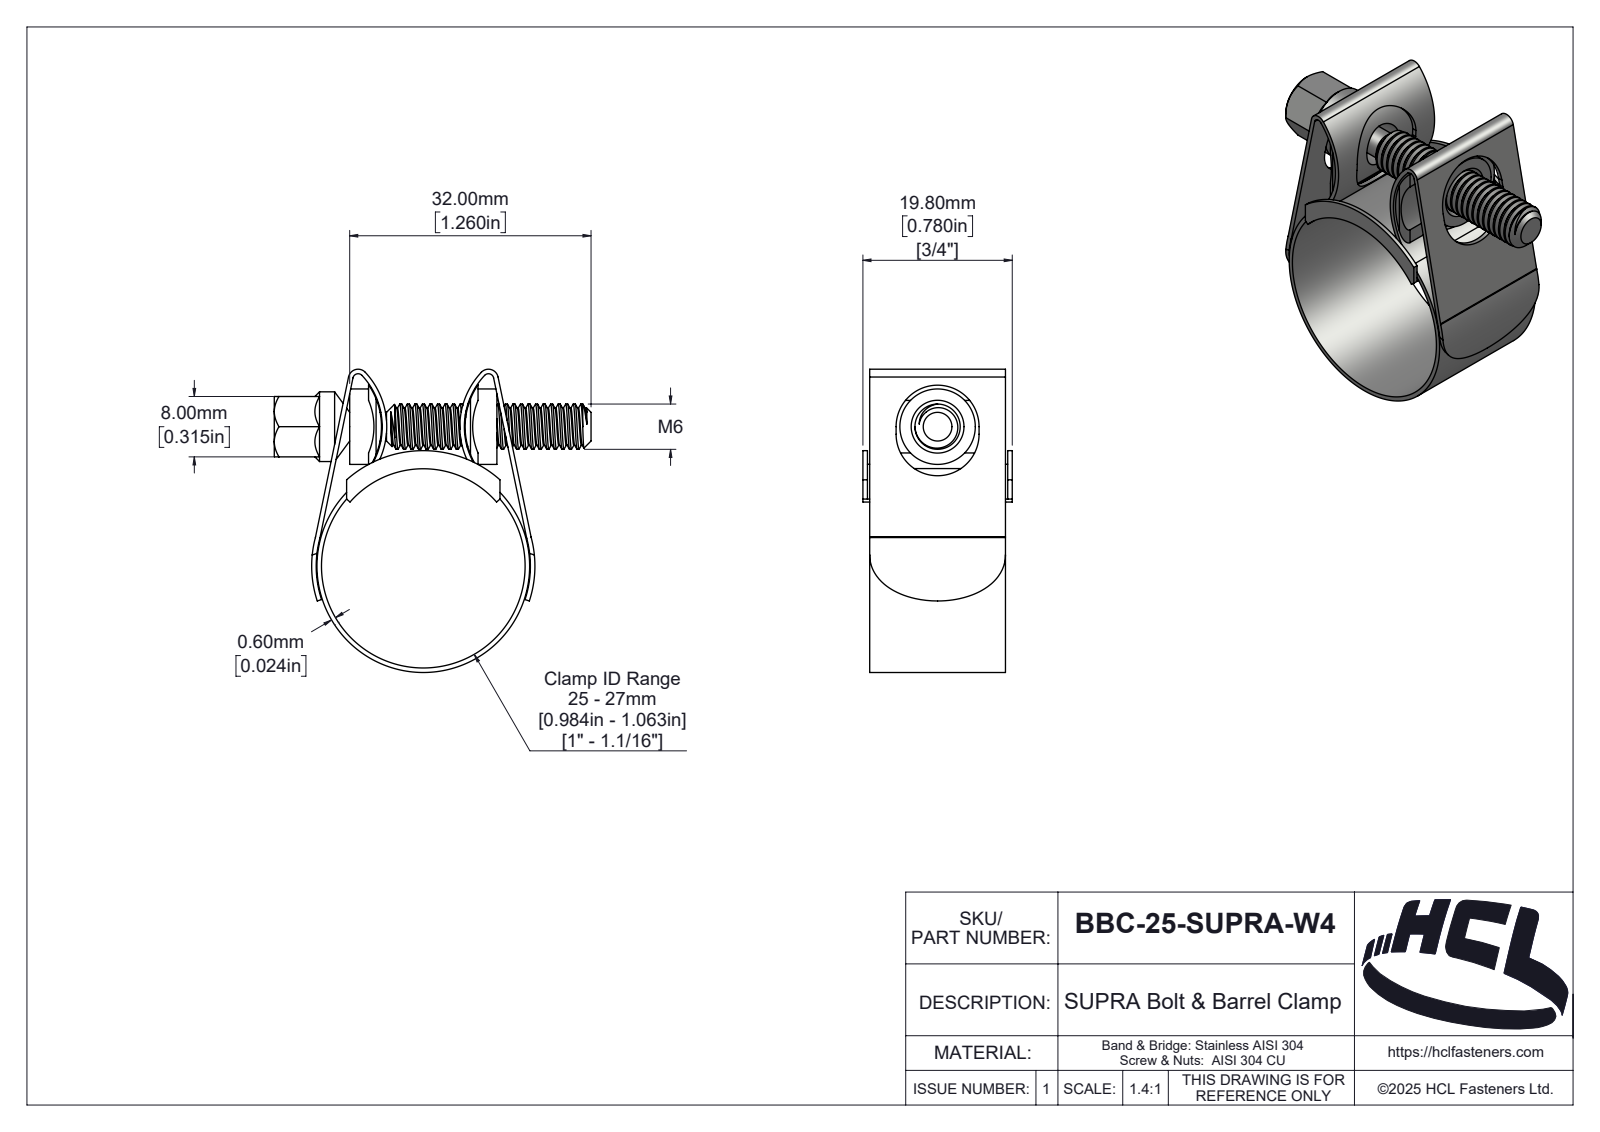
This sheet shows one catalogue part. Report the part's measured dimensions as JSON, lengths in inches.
{"part_name": "BBC-25-SUPRA-W4", "step_written_by": "SolidWorks 2025 (AUTOMOTIVE_DESIGN)", "units": "inches", "bodies": {"solids": 5, "faces": 288, "planar": 44, "cylindrical": 164, "other": 80}, "overall_size": [1.654, 1.582, 0.78], "volume_in3": 0.219, "surface_area_in2": 13.33, "round_holes": [[1.063, 1]], "round_bosses_or_shafts": [[0.394, 1], [0.364, 1], [0.236, 1], [0.15, 1]], "partial_cylinders_radius": [[0.039, 4], [0.028, 2], [0.051, 2], [0.079, 2], [0.102, 2], [0.217, 2], [0.348, 2], [0.387, 2]], "face_to_face_distances": [0.024, 0.035, 0.744, 0.709, 0.756, 0.72, 0.098, 0.67, 0.315, 0.732]}
